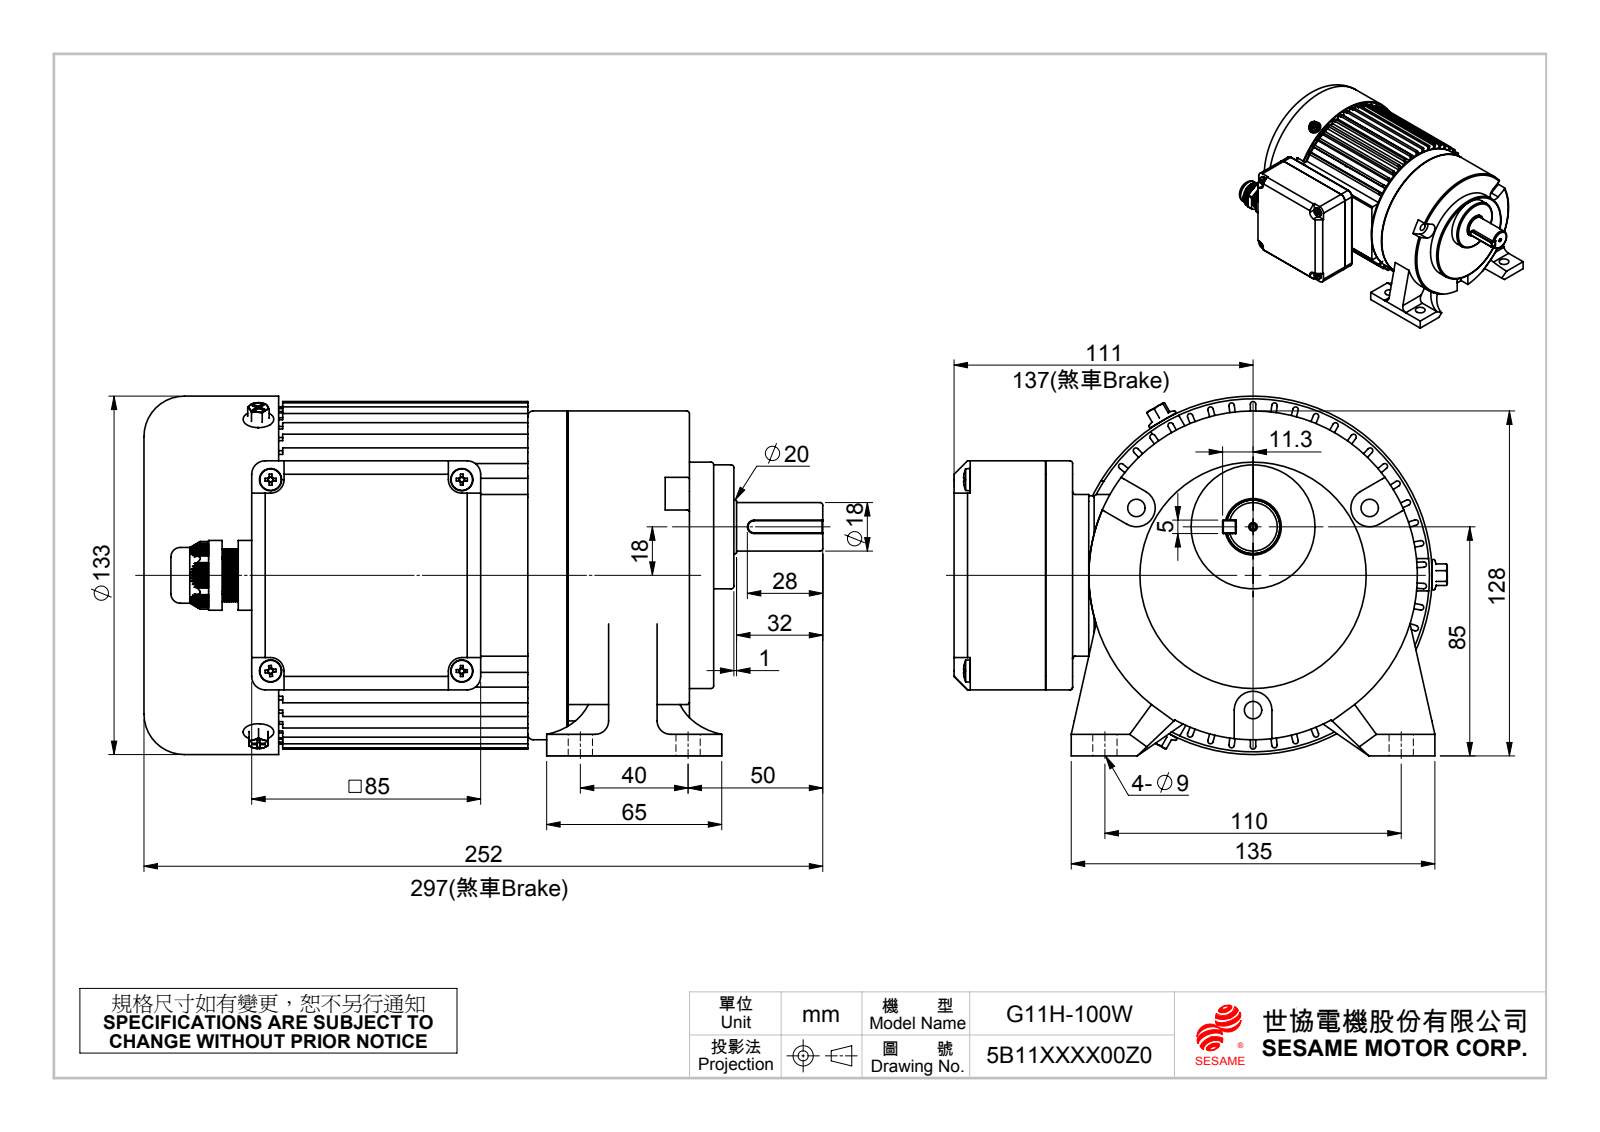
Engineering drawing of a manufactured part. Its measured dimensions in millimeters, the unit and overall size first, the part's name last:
Units: millimetres
Overall size (bounding box): 252 × 183.11 × 133.5
Round holes (diameter × count): ⌀5 ×11, ⌀3.3 ×9, ⌀8 ×4, ⌀9 ×4, ⌀4.2 ×3, ⌀6.5 ×3, ⌀11 ×3, ⌀2 ×1, ⌀7.5 ×1, ⌀10.8 ×1, ⌀16.5 ×1, ⌀20 ×1
Round bosses / shafts (diameter × count): ⌀8.3 ×4, ⌀4 ×4, ⌀5 ×3, ⌀133 ×1, ⌀131 ×1, ⌀122 ×1, ⌀118 ×1, ⌀110.4 ×1
Partial cylindrical surfaces — rounded edges, fillets, slot ends (radius × count): R1 ×76, R5 ×10, R1.03 ×8, R2.75 ×6, R2 ×4, R2.55 ×4, R3.55 ×4, R22.5 ×4
Main face-to-face distances: 2, 3, 92, 10, 125, 18, 20, 95, 115, 105
Hole centre spacings: 45, 71, 50, 86.6, 11, 11.5, 14.66, 14.79
Volume: 2 421 000 mm³ · Surface area: 362 073 mm²
Bodies: 19 solids, 2664 faces (820 planar, 838 cylindrical, 1006 other)
Part name (STEP PRODUCT): G11HBOX1; G11-200C1; 出線盒下蓋; 出線盒上蓋 (+8 more)
STEP written by: SolidWorks 2010 (CONFIG_CONTROL_DESIGN)
